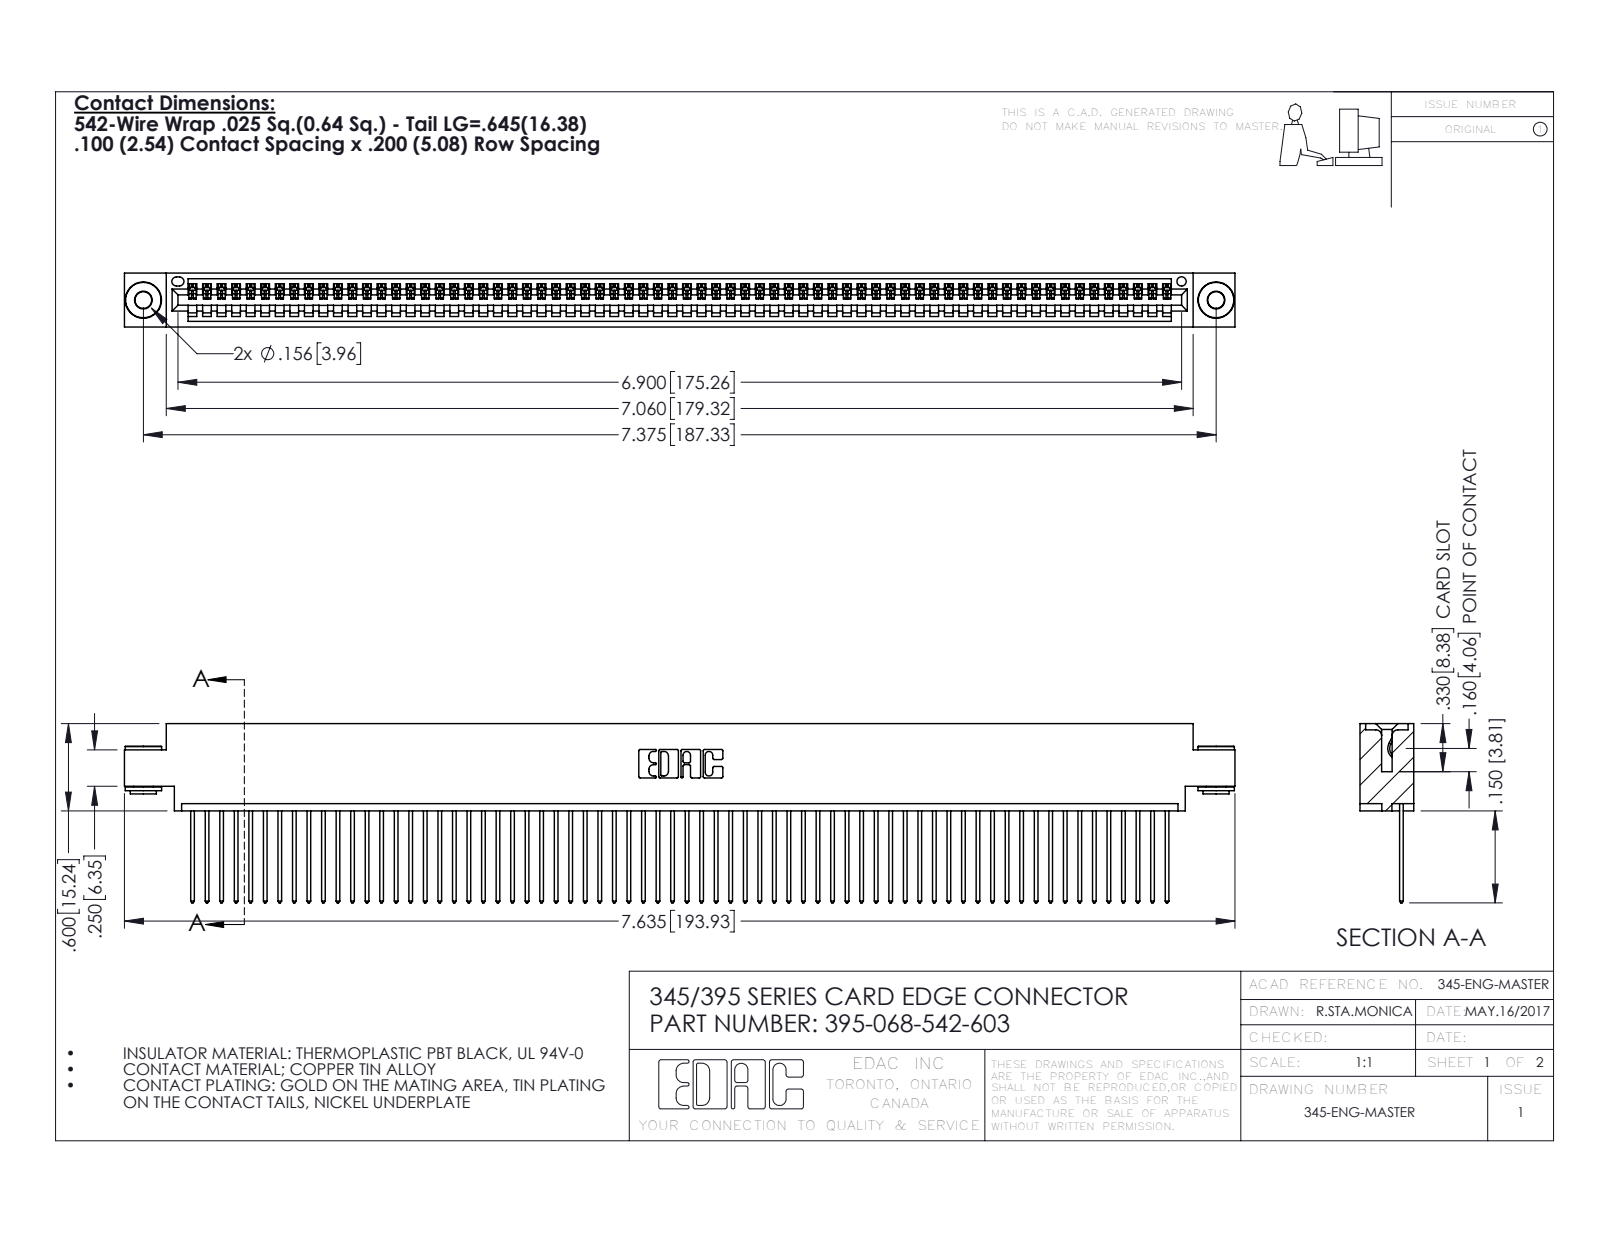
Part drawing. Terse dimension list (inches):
name: 395-068-542-603; 345-292-001_345-293-142; 345-250-002_345-250-002-102; 345 Part_0.170 Offset - 0.156 Dia-TH
written by: SolidWorks 2016 (CONFIG_CONTROL_DESIGN)
unit: in
bodies: 71 solids, 4112 faces (2814 planar, 1290 cylindrical, 8 other)
size: 7.635 × 1.232 × 0.37
volume: 1.141 in³; area: 41.06 in²
holes: 2× ⌀0.116, 2× ⌀0.156, 1× ⌀0.064
bosses: 2× ⌀0.25, 2× ⌀0.18, 2× ⌀0.136
rounds: 136× R0.006, 136× R0.01, 22× R0.01, 6× R0.007, 6× R0.031, 3× R0.026, 2× R0.031, 2× R0.04
face distances: 0.072, 0.298, 0.37, 0.098, 0.272, 0.025, 0.2, 0.225, 0.175, 0.149
hole spacings: 0.27, 7.139, 7.375
